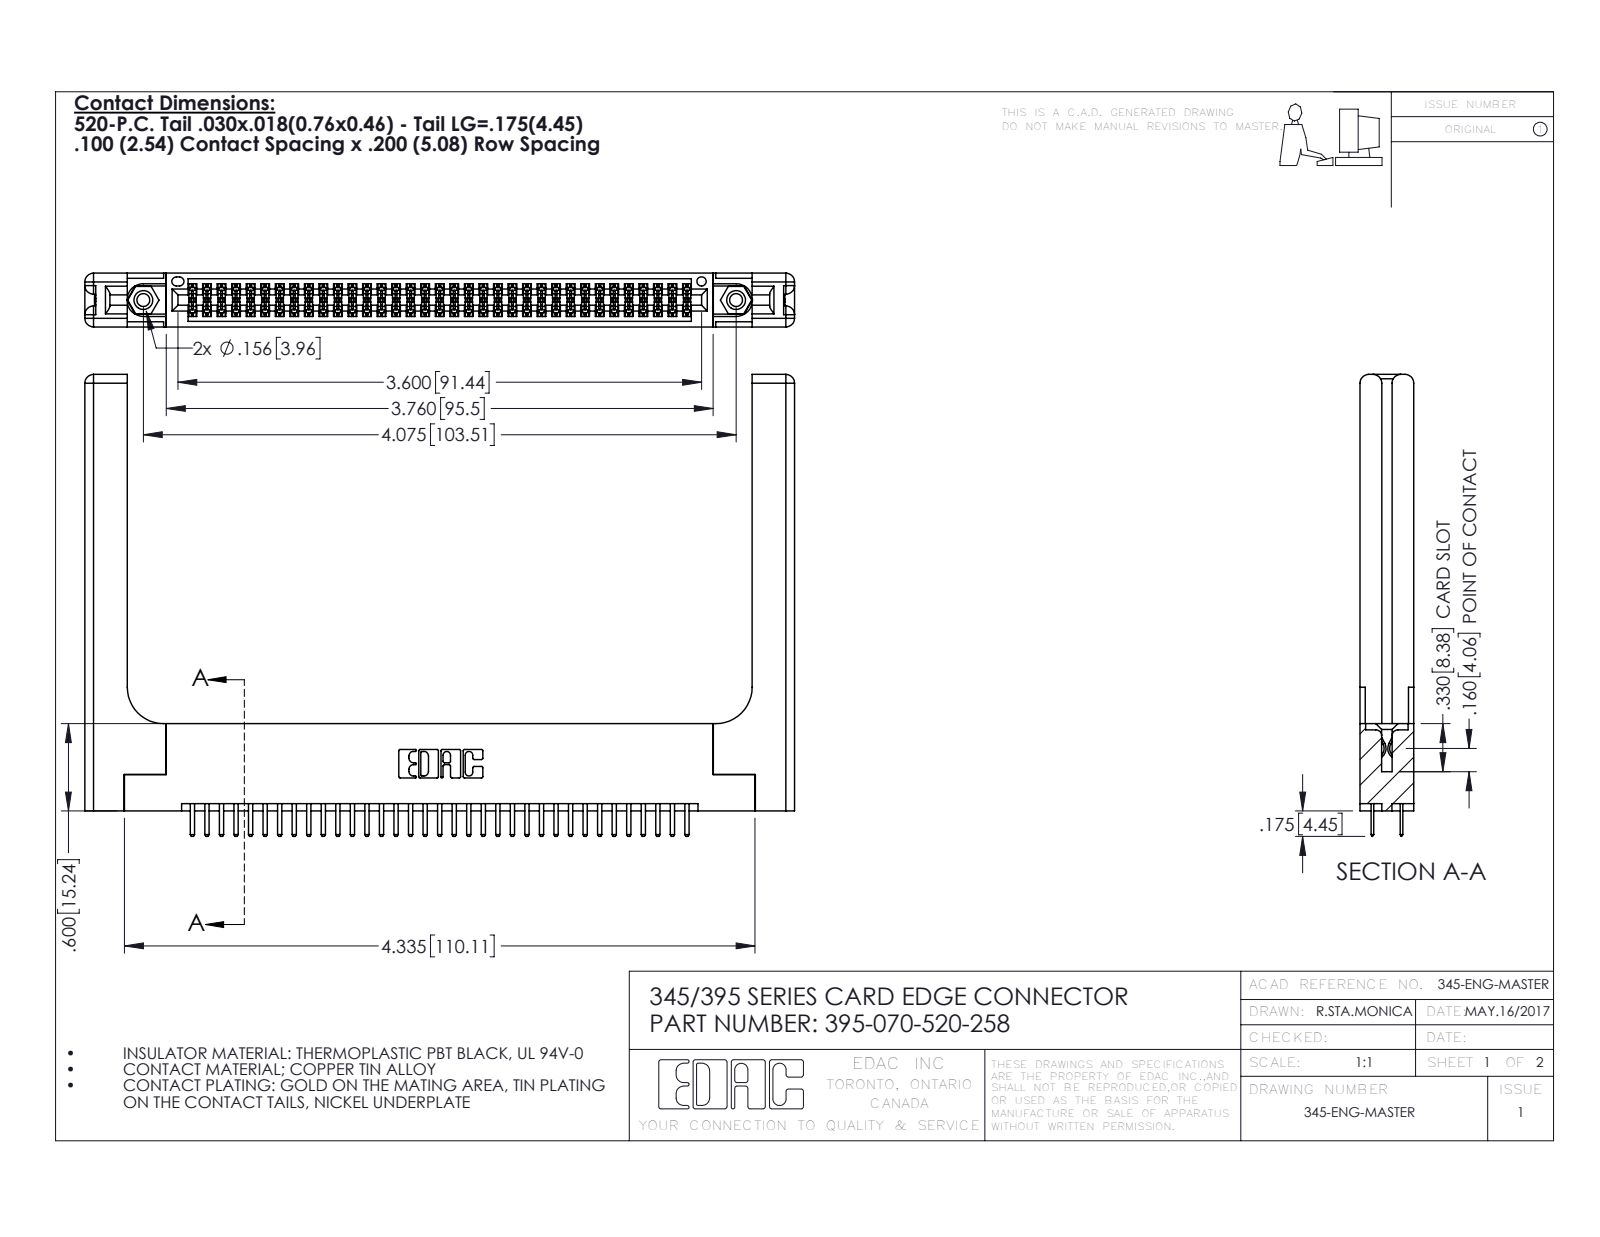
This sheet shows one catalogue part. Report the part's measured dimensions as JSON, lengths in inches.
{"part_name": "345-292-001_345-293-120; 345-220-058_345-220-058; 395-070-520-258; 345-250-001_345-250-001-102 (+1 more)", "step_written_by": "SolidWorks 2016 (CONFIG_CONTROL_DESIGN)", "units": "inches", "bodies": {"solids": 75, "faces": 4162, "planar": 2678, "cylindrical": 1424, "other": 60}, "overall_size": [4.879, 3.175, 0.37], "volume_in3": 1.246, "surface_area_in2": 34.89, "round_holes": [[0.089, 2], [0.125, 2], [0.156, 2], [0.064, 1]], "round_bosses_or_shafts": [[0.155, 2]], "partial_cylinders_radius": [[0.006, 105], [0.01, 74], [0.01, 22], [0.06, 16], [0.007, 6], [0.031, 6], [0.026, 3], [0.014, 2]], "face_to_face_distances": [0.37, 0.072, 0.298, 0.2, 0.098, 0.272, 0.025, 0.225, 0.148, 0.15], "hole_center_spacings": [0.27, 3.839, 4.075]}
